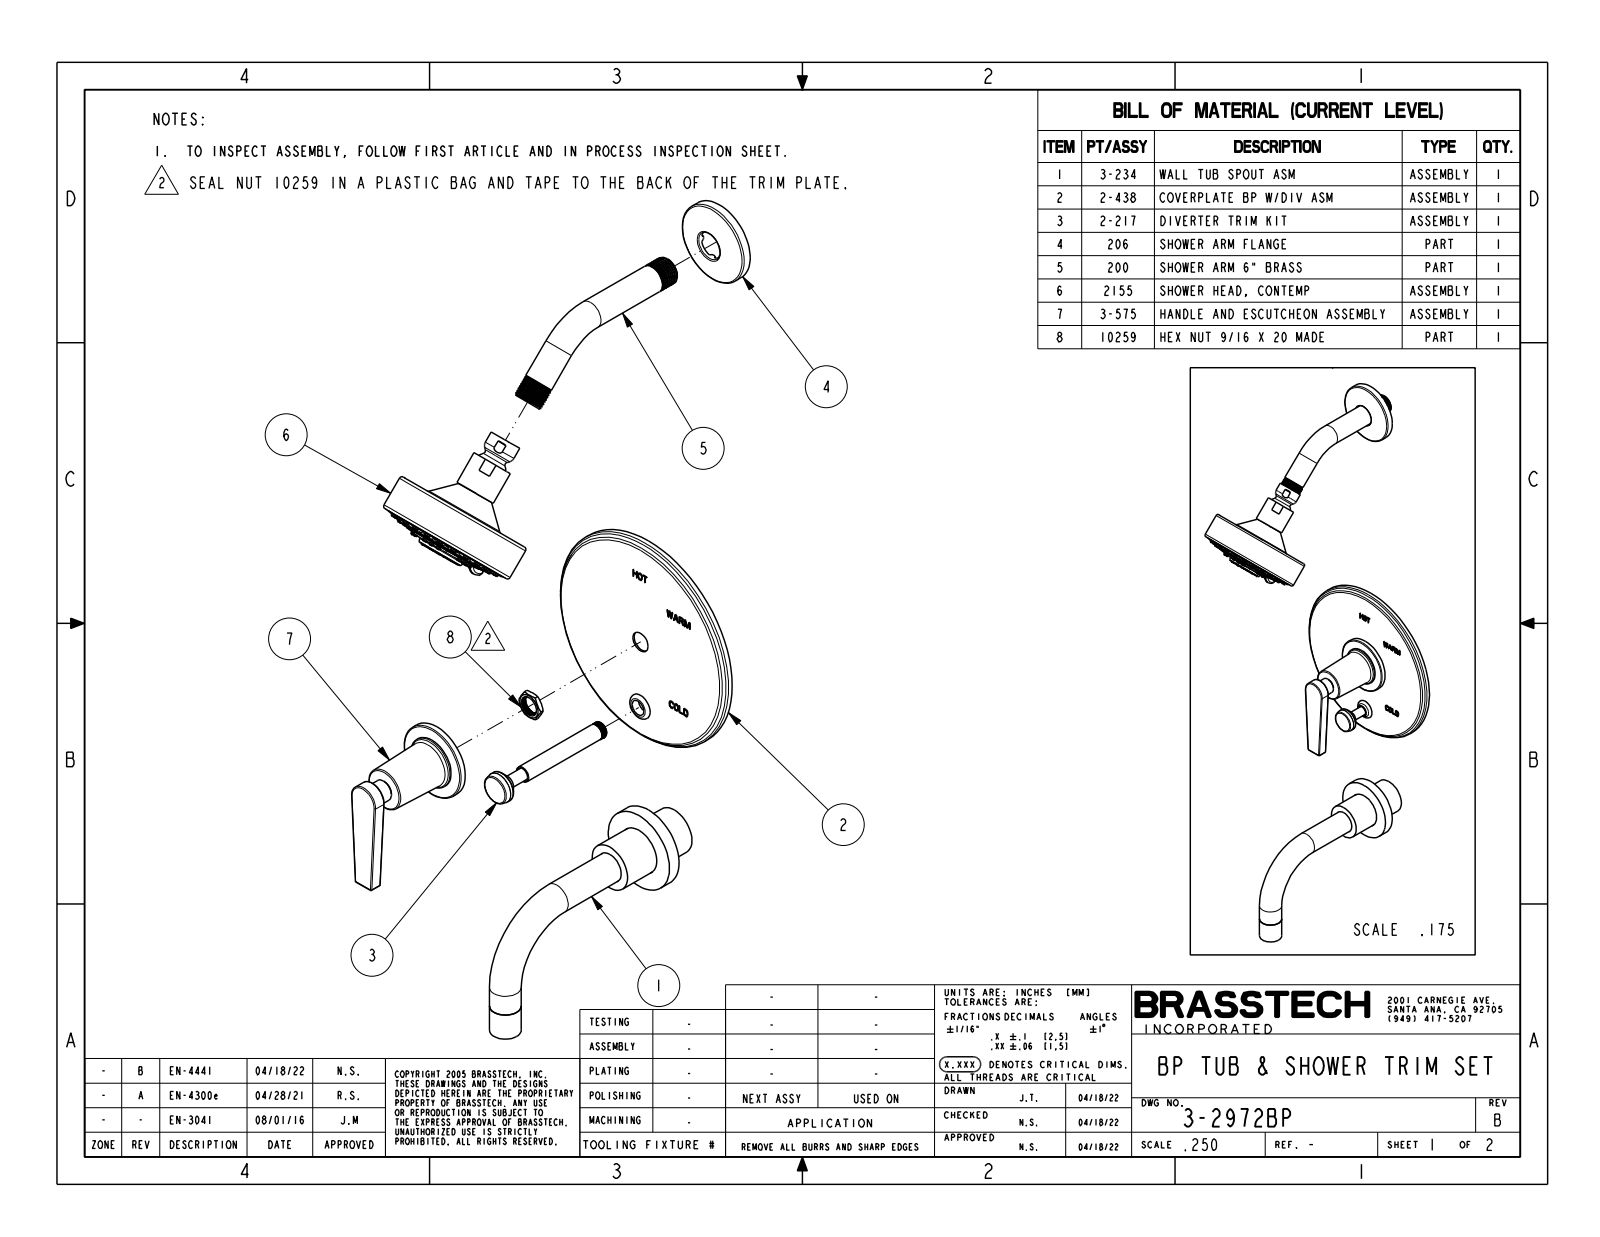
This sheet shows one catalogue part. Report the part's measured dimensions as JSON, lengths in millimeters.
{"part_name": "3-2972BP", "step_written_by": "CREO PARAMETRIC BY PTC INC, 2018400 (CONFIG_CONTROL_DESIGN)", "units": "millimeters", "bodies": {"solids": 3, "faces": 1398, "planar": 410, "cylindrical": 229, "other": 759}, "overall_size": [600.2, 207.6, 165.1], "volume_mm3": 722000, "surface_area_mm2": 131800, "round_holes": [[1.5, 8], [11.8, 1], [23.5, 1]], "round_bosses_or_shafts": [[3.6, 39], [4.2, 23], [22.2, 2], [20.7, 2], [165.1, 1], [101.6, 1], [94.6, 1], [60.5, 1]], "partial_cylinders_radius": [[0.8, 8], [2, 8], [0.5, 2], [3.5, 1], [11.7, 1], [12, 1], [13, 1], [16, 1]], "face_to_face_distances": [8, 1.6, 9.5, 3.2, 4.7, 12.7, 80.8, 72.9, 71.3, 68.1], "hole_center_spacings": [11.3, 14.7, 20.8, 20.8, 27.2, 11.3, 14.7, 27.2]}
